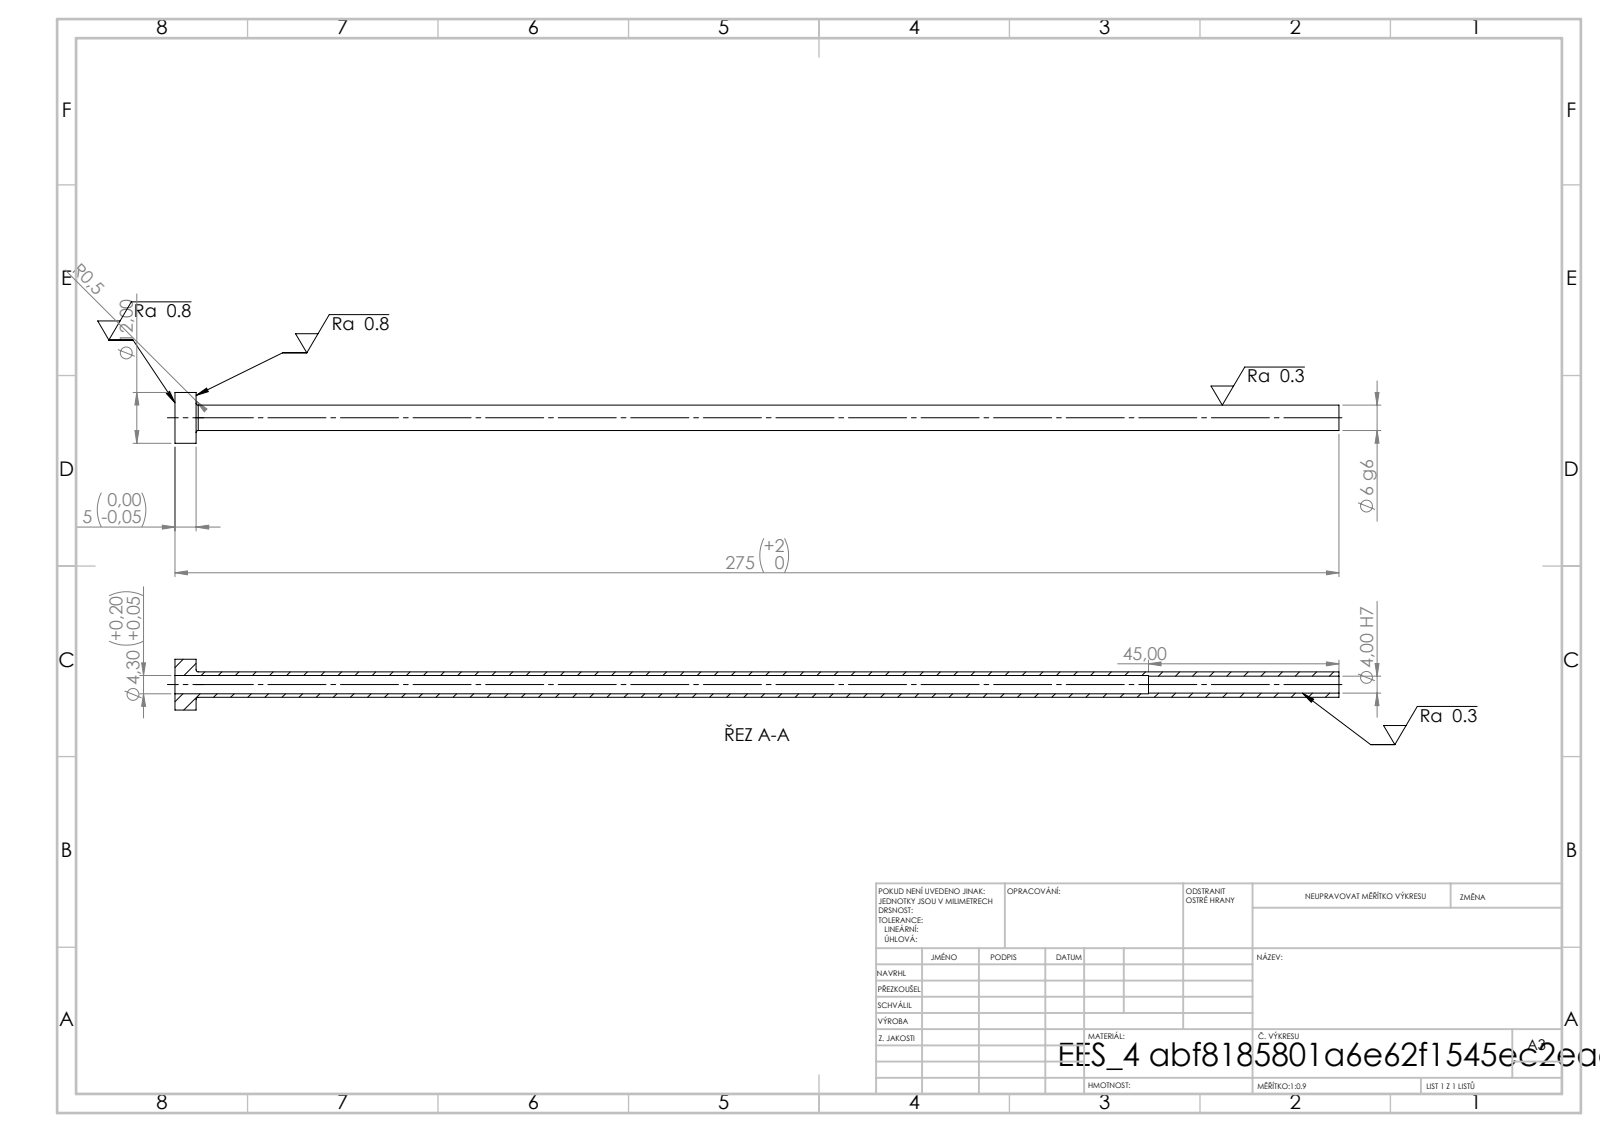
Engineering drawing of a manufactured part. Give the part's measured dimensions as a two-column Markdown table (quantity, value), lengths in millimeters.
| quantity | value |
| --- | --- |
| STEP written by | SolidWorks 2019 (CONFIG_CONTROL_DESIGN) |
| units | millimeters |
| bodies | 1 solid, 14 faces (4 planar, 8 cylindrical, 2 other) |
| overall size | 275 × 12 × 12 |
| volume | 4 295 mm³ |
| surface area | 9 148 mm² |
| round holes (diameter × count) | 4 × 1, 4.3 × 1 |
| round bosses / shafts (diameter × count) | 12 × 1, 6 × 1 |
| main face-to-face distances | 5, 275, 270, 230, 225, 45 |
